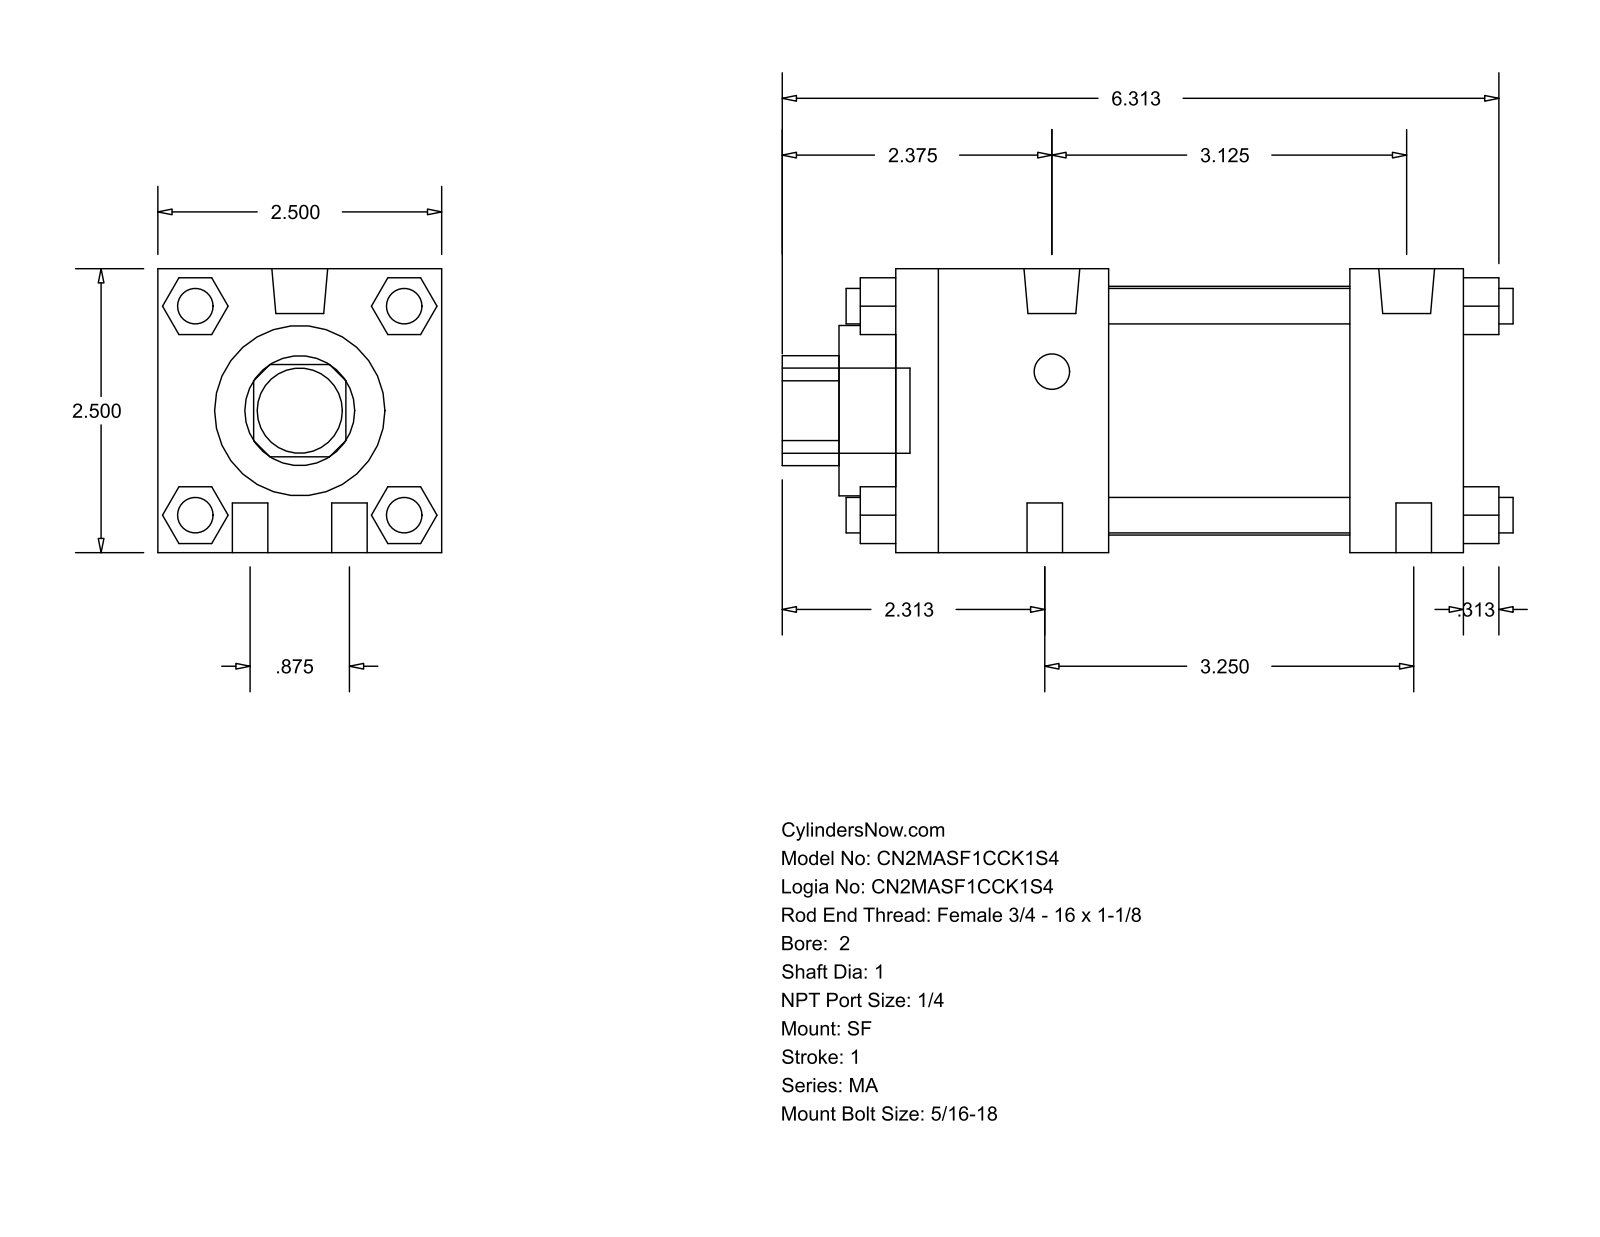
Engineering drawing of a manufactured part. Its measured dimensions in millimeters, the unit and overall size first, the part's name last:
Units: millimetres
Overall size (bounding box): 163.51 × 63.5 × 63.5
Round holes (diameter × count): ⌀25.4 ×1, ⌀38.1 ×1, ⌀55.63 ×1
Round bosses / shafts (diameter × count): ⌀7.94 ×10, ⌀12.49 ×2, ⌀19.05 ×1
Partial cylindrical surfaces — rounded edges, fillets, slot ends (radius × count): R12.29 ×1
Main face-to-face distances: 63.5, 127, 12.7, 25.4, 101.6, 47.63, 53.97, 79.37, 40.47, 23.37
Bodies: 0 solids, 124 faces (94 planar, 30 cylindrical, 0 other)
Part name (STEP PRODUCT): MA_SF__0200_1
STEP written by: GSSL Pune (CONFIG_CONTROL_DESIGN)
